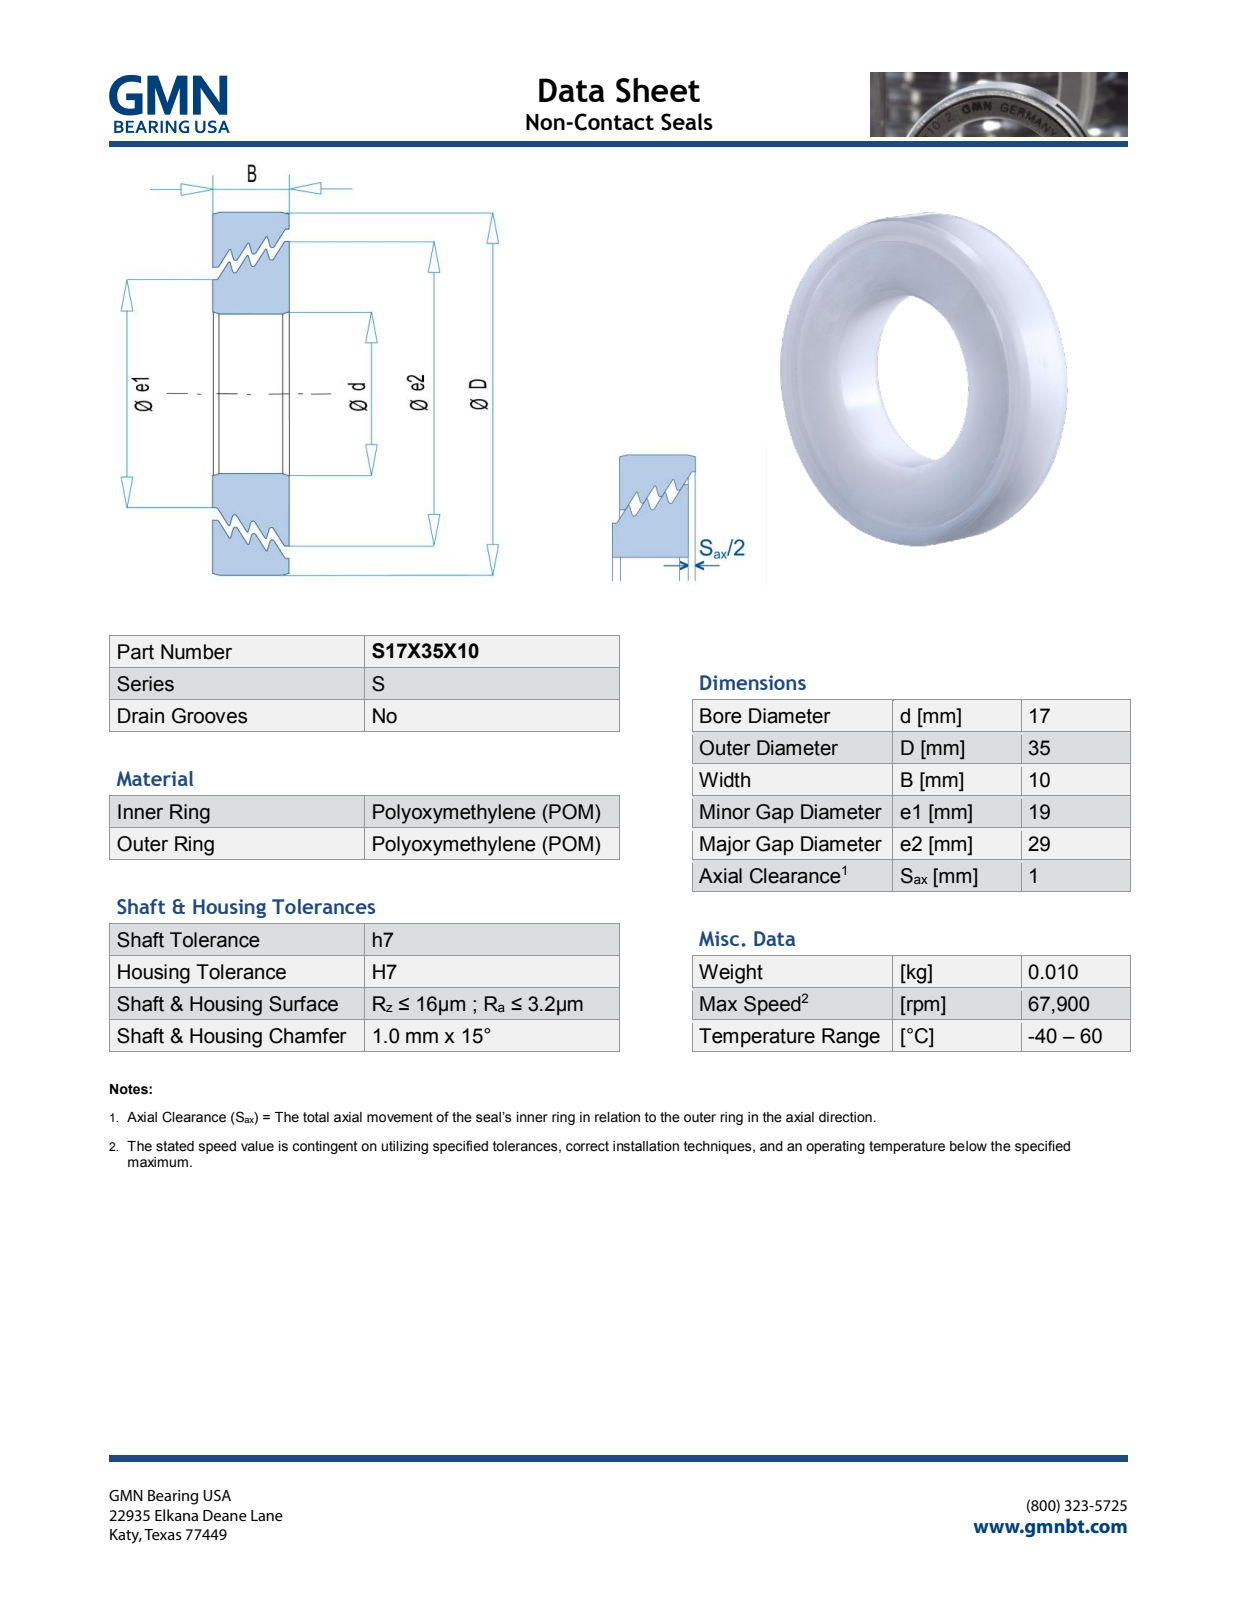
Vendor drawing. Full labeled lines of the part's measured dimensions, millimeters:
Part name (STEP PRODUCT): S17X35X10_PRT
STEP written by: PRO/ENGINEER BY PARAMETRIC TECHNOLOGY CORPORATION, 2013150 (AUTOMOTIVE_DESIGN)
Units: millimetres
Bodies: 2 solids, 608 faces (528 planar, 12 cylindrical, 68 other)
Overall size (bounding box): 35 × 35 × 10.07
Volume: 6 673 mm³ · Surface area: 6 127 mm²
Round holes (diameter × count): ⌀17 ×1, ⌀20.63 ×1, ⌀30.63 ×1
Round bosses / shafts (diameter × count): ⌀35 ×1, ⌀29 ×1, ⌀19 ×1
Main face-to-face distances: 10, 10.07, 1.53, 1.34, 1.14, 1.54, 1.08, 0.65, 0.68, 1.15
